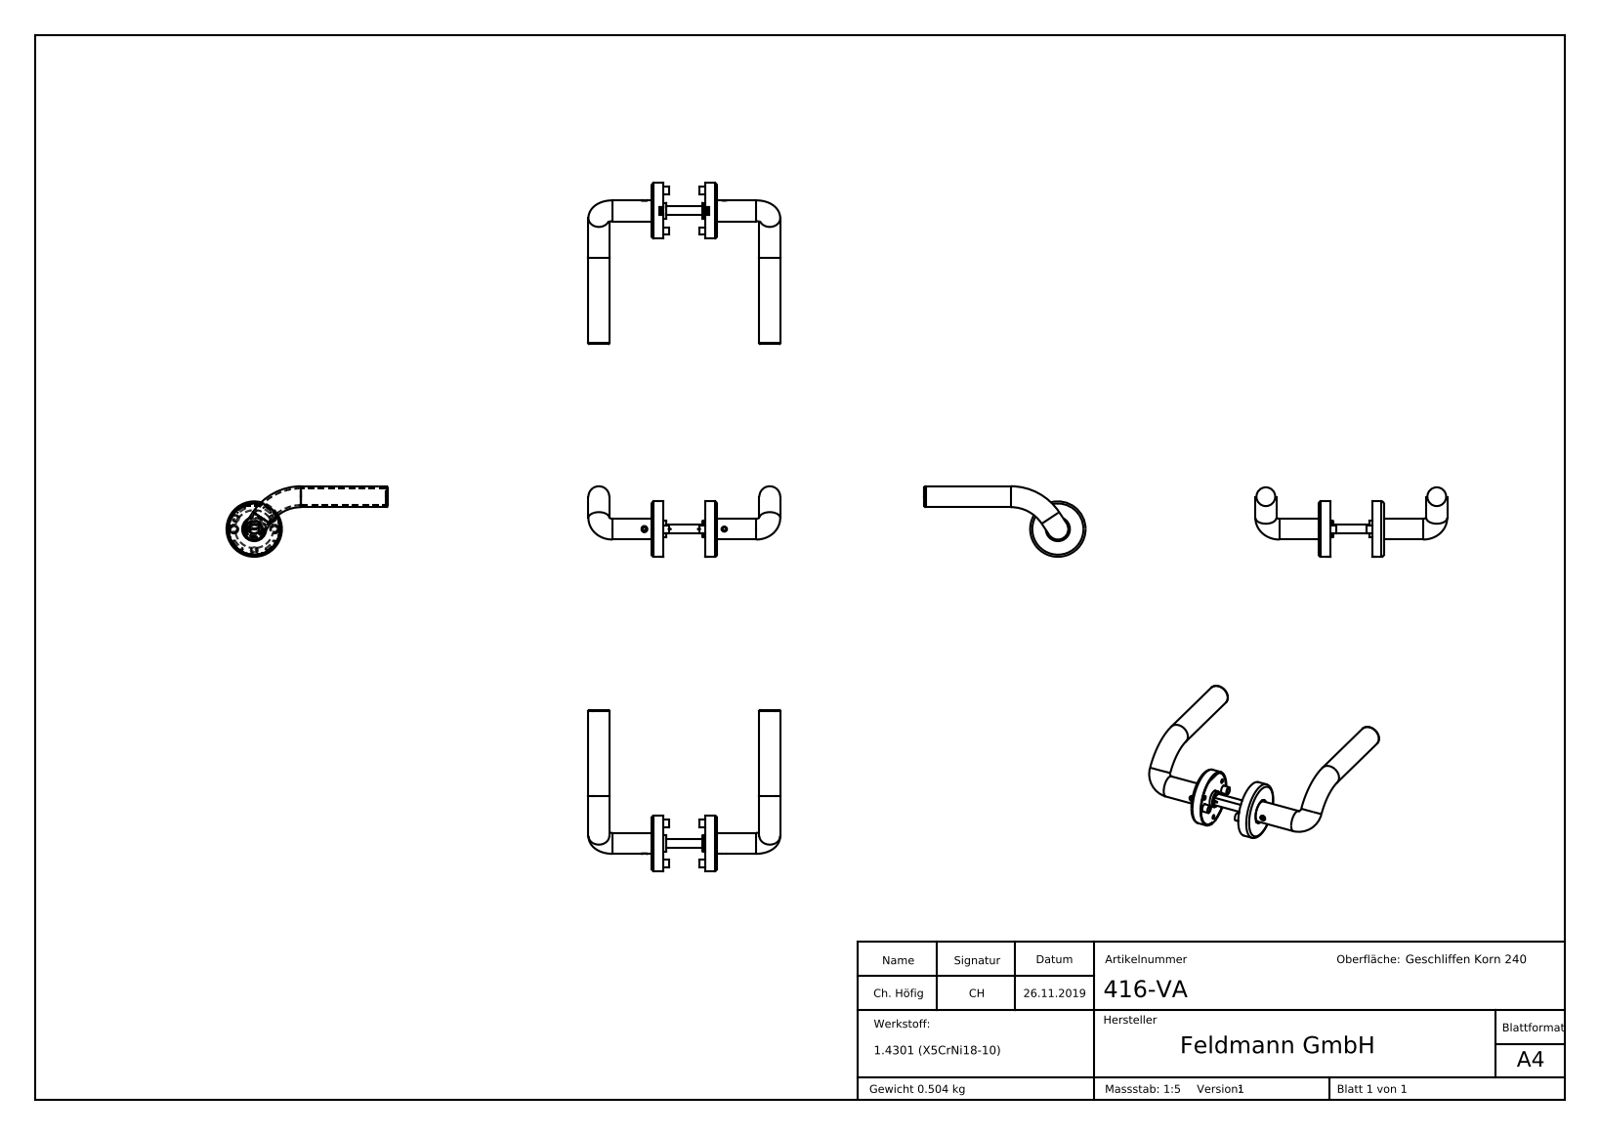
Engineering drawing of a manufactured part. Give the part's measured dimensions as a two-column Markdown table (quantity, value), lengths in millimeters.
| quantity | value |
| --- | --- |
| part name | 4XX-VA Teil2; 416-VA; DIN914; 4XX-VA Teil1_416-VA Teil1 (+8 more) |
| STEP written by | SolidWorks 2015 (CONFIG_CONTROL_DESIGN) |
| units | millimeters |
| bodies | 13 solids, 865 faces (503 planar, 124 cylindrical, 238 other) |
| overall size | 70000 × 5999.86 × 5999.7 |
| volume | 112 630 mm³ |
| surface area | 103 016 mm² |
| round holes (diameter × count) | 15.7 × 4, 3.7 × 3, 5 × 3, 6.1 × 3, 5.5 × 2, 7.3 × 2, 8 × 2, 15.4 × 1, 16.2 × 1, 22.6 × 1 |
| round bosses / shafts (diameter × count) | 19.6 × 4, 7.1 × 2, 6 × 2, 52 × 1, 50 × 1, 49.8 × 1, 21.4 × 1, 15.2 × 1 |
| partial cylindrical surfaces (radius × count) | 1 × 4, 4.5 × 1, 17.85 × 1, 21 × 1, 23 × 1 |
| main face-to-face distances | 1, 60, 10.5, 50.5, 9.5, 49.5, 8.1, 40, 0.8, 8 |
| hole center spacings | 20, 34.64, 52.42, 10.14, 19, 27.59, 37.67, 45 |
